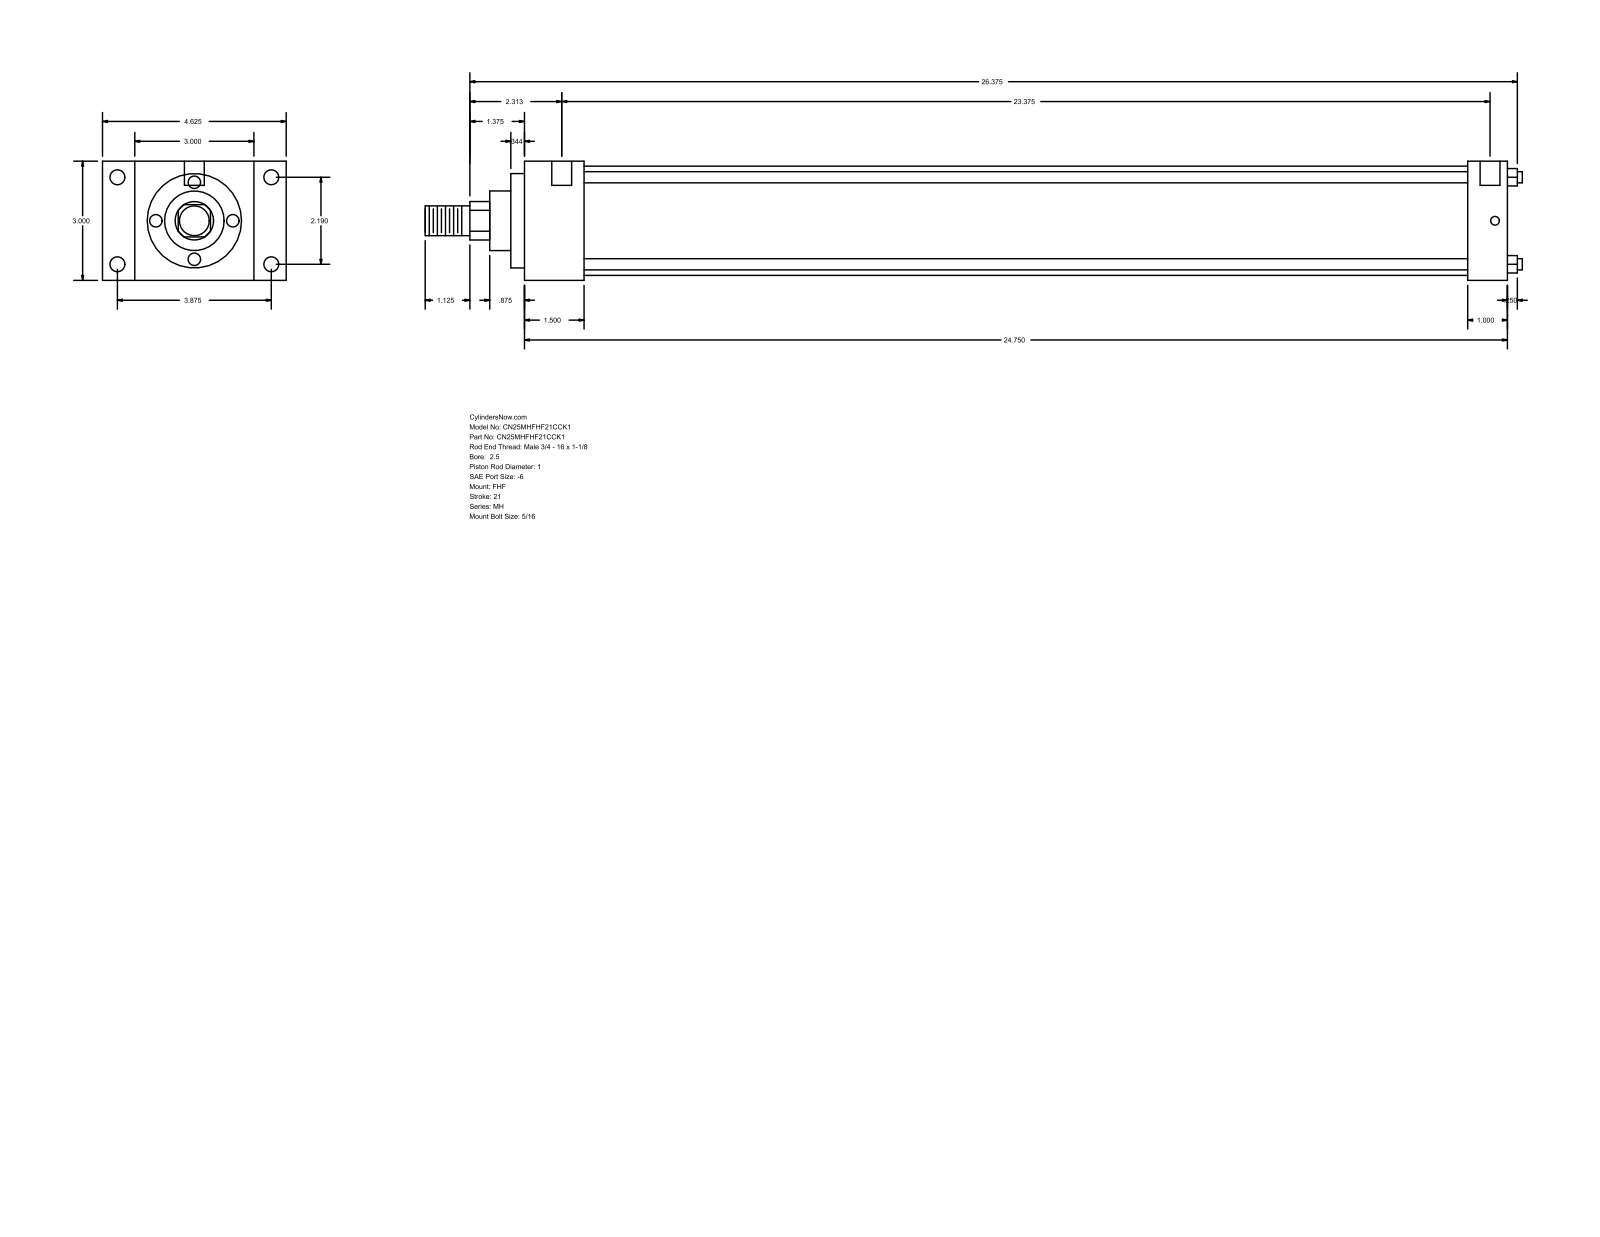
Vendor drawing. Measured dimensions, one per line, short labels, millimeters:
name: MH_FHF__0250_1
written by: GSSL Pune (CONFIG_CONTROL_DESIGN)
unit: mm
bodies: 0 solids, 90 faces (61 planar, 29 cylindrical, 0 other)
size: 701.67 × 117.47 × 76.2
holes: 4× ⌀5.56, 4× ⌀9.53, 2× ⌀12.7
bosses: 4× ⌀7.14, 1× ⌀69.85, 1× ⌀60.33, 1× ⌀38.1, 1× ⌀25.4, 1× ⌀19.05
rounds: 1× R12.29
face distances: 76.2, 628.66, 38.11, 590.55, 20.64, 96.84, 117.48, 603.25, 565.14, 25.41
hole spacings: 55.62, 98.42, 113.05, 601.66, 3.18, 4.76, 593.72, 596.9
